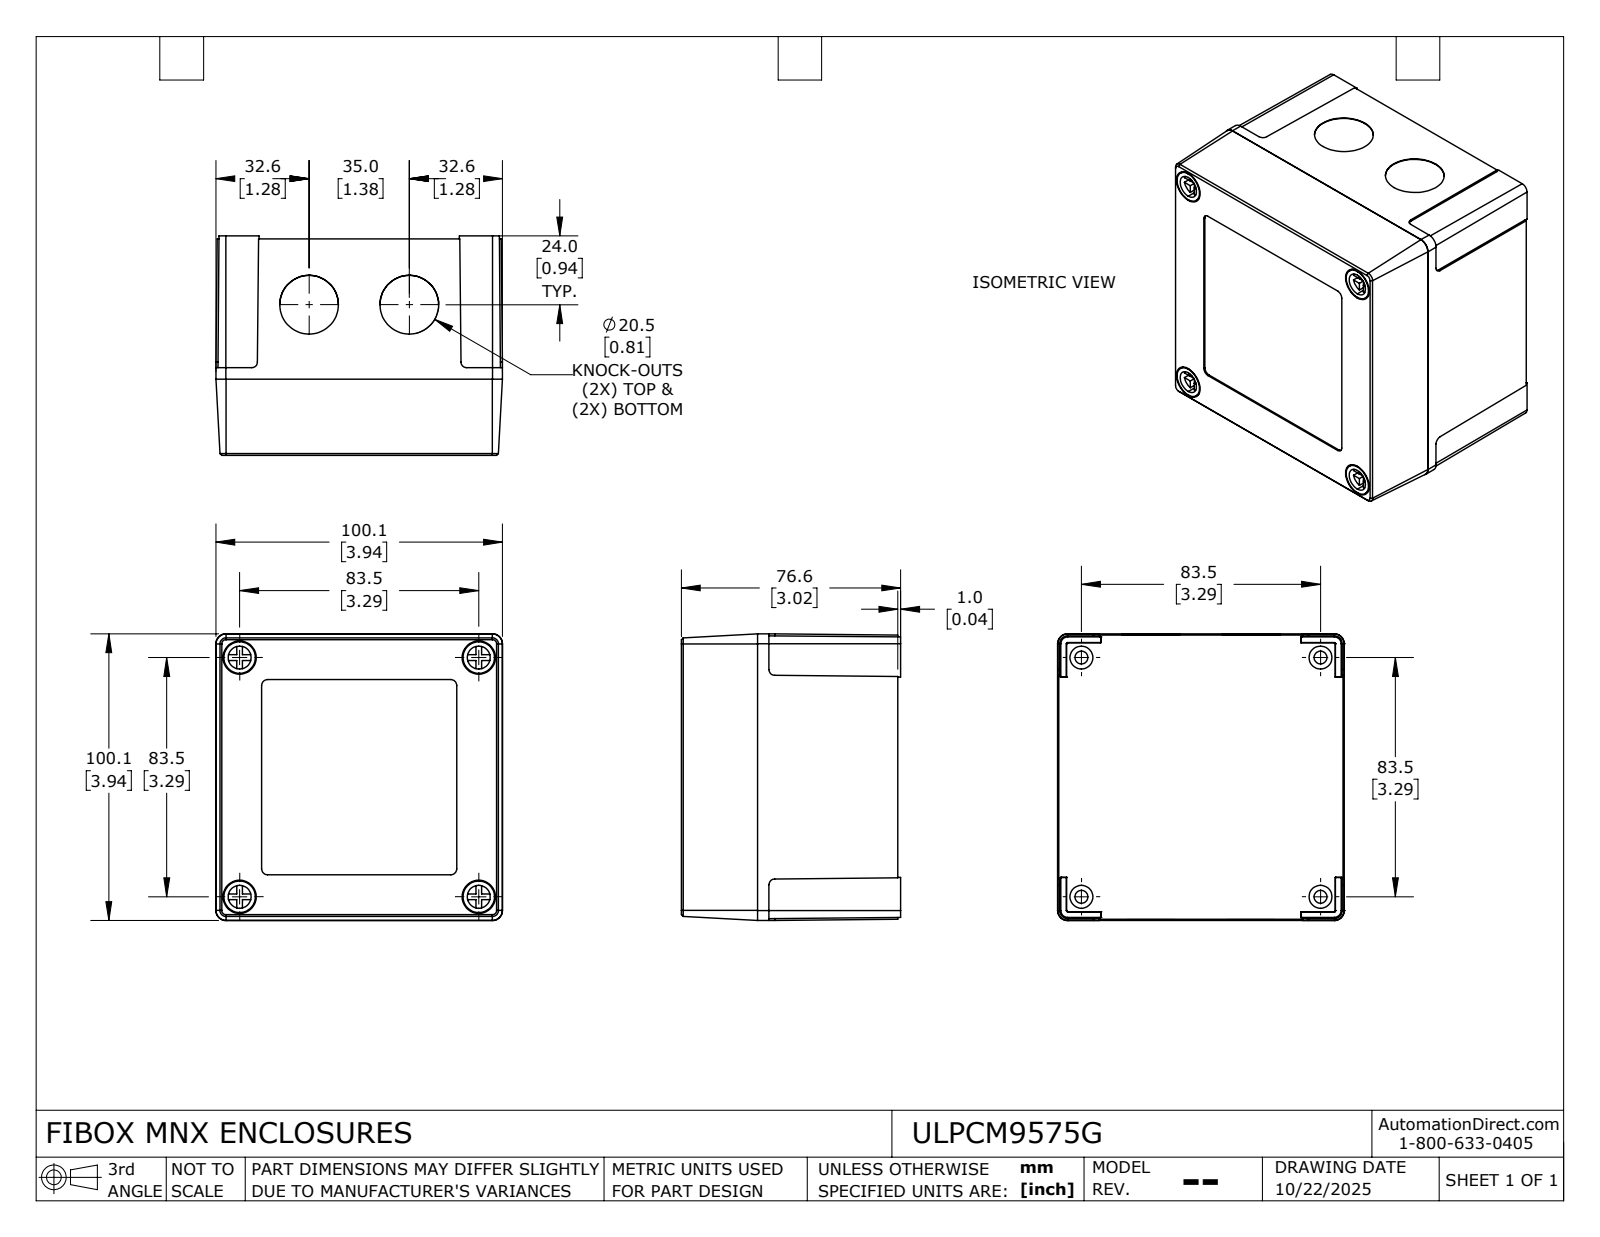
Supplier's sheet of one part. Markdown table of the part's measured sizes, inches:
| quantity | value |
| --- | --- |
| part name | ULPCM9575G_Default |
| STEP written by | SolidWorks 2024 (CONFIG_CONTROL_DESIGN) |
| units | inches |
| bodies | 6 solids, 510 faces (294 planar, 176 cylindrical, 40 other) |
| overall size | 3.941 × 3.941 × 3.016 |
| volume | 11.48 in³ |
| surface area | 169.8 in² |
| round holes (diameter × count) | 0.094 × 6, 0.118 × 6, 0.126 × 6, 0.157 × 6, 0.177 × 4, 0.315 × 4, 0.457 × 4, 0.807 × 4 |
| round bosses / shafts (diameter × count) | 0.315 × 6, 0.433 × 4, 0.283 × 4, 0.236 × 2 |
| partial cylindrical surfaces (radius × count) | 0.079 × 8, 0.056 × 6, 0.021 × 4, 0.03 × 4, 0.118 × 4, 0.197 × 4, 0.023 × 2 |
| main face-to-face distances | 0.165, 2.878, 0.118, 2.76, 0.079, 2.839, 2.957, 0.02, 2.858, 0.098 |
| hole center spacings | 0.803, 0.886, 1.159, 1.354, 1.461, 1.665, 1.824, 1.931 |
